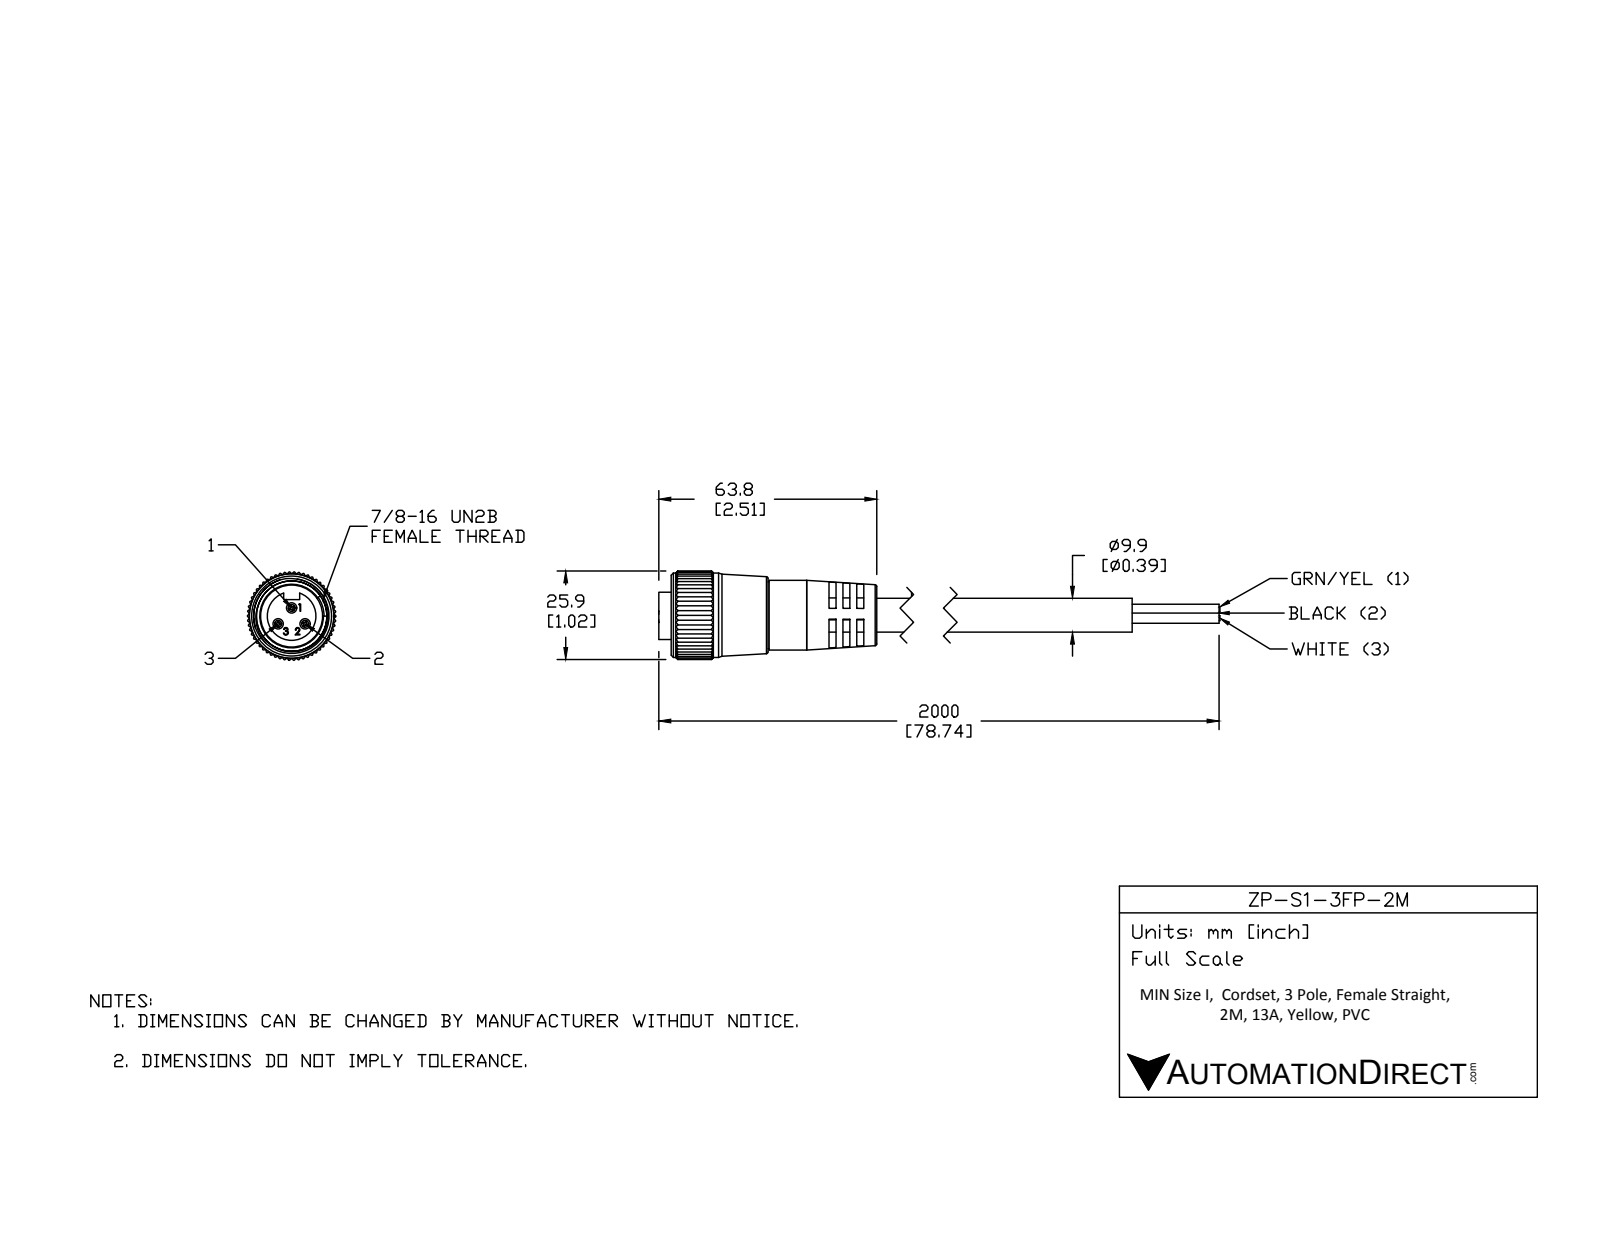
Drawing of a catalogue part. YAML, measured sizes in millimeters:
part_name: "ZP-S1-3FP-2M"
step_written_by: "SolidWorks 2015 (AUTOMOTIVE_DESIGN)"
units: millimeters
bodies: {solids: 2, faces: 540, planar: 192, cylindrical: 306, other: 42}
overall_size: [108.72, 52.91, 25.84]
volume: 26739
surface_area: 11837
round_holes:
  - {diameter: 3.05, count: 3}
  - {diameter: 18.14, count: 1}
  - {diameter: 20.58, count: 1}
  - {diameter: 21, count: 1}
round_bosses_or_shafts:
  - {diameter: 9.91, count: 2}
  - {diameter: 24.68, count: 1}
  - {diameter: 20.4, count: 1}
  - {diameter: 19.5, count: 1}
  - {diameter: 14.22, count: 1}
partial_cylinders:
  - {radius: 0.25, count: 165}
  - {radius: 5.25, count: 1}
  - {radius: 12.93, count: 1}
face_to_face_distances: [4.03, 2, 2.03, 6.03, 8.06, 13.87, 11.87, 9.84, 7.84, 6.06]
hole_center_spacings: [6.07, 2.36, 4.53, 4.54, 7.87]
